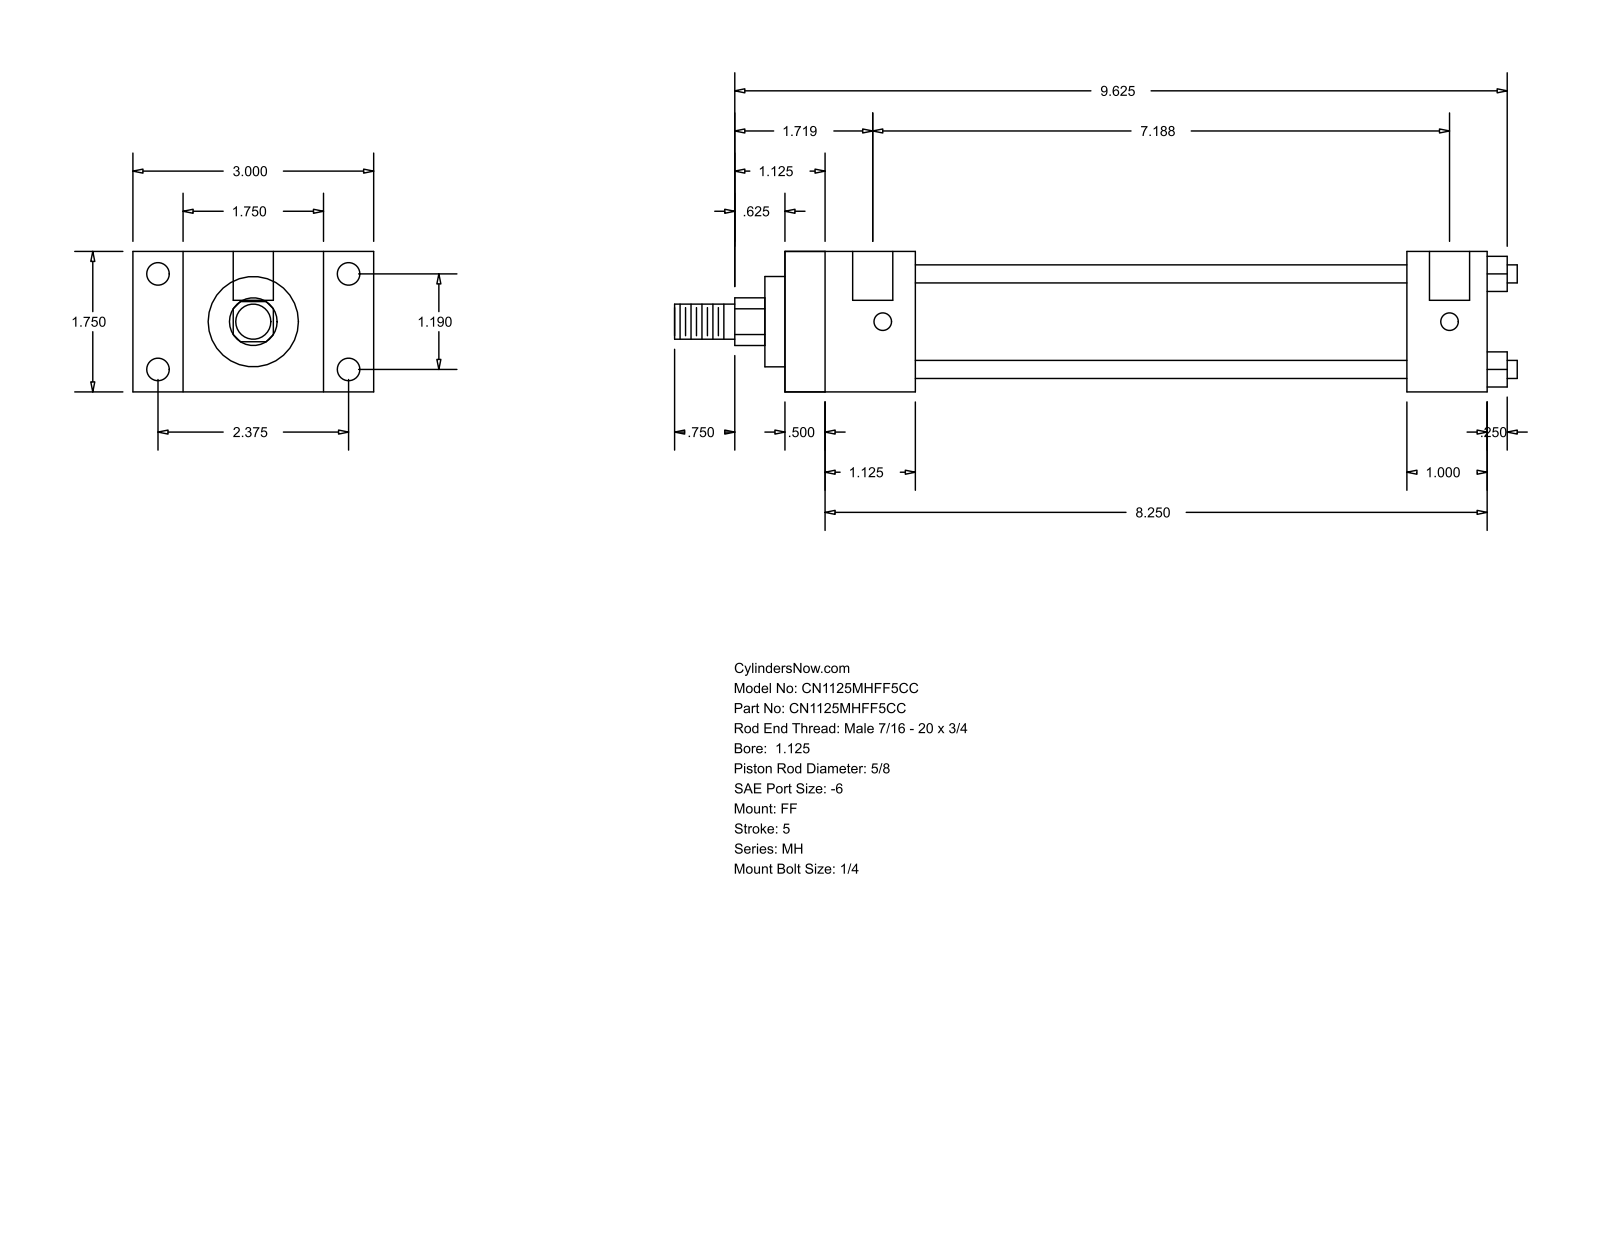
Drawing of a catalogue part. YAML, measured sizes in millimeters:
part_name: "MH_FF__0112_0.625"
step_written_by: "GSSL Pune (CONFIG_CONTROL_DESIGN)"
units: millimeters
bodies: {solids: 0, faces: 92, planar: 64, cylindrical: 28, other: 0}
overall_size: [266.7, 76.2, 44.45]
round_holes:
  - {diameter: 5.56, count: 4}
  - {diameter: 7.14, count: 4}
  - {diameter: 12.7, count: 2}
round_bosses_or_shafts:
  - {diameter: 5.71, count: 4}
  - {diameter: 34.92, count: 1}
  - {diameter: 28.57, count: 1}
  - {diameter: 15.88, count: 1}
  - {diameter: 11.11, count: 1}
partial_cylinders:
  - {radius: 7.54, count: 1}
face_to_face_distances: [44.46, 222.24, 12.69, 209.55, 15.87, 28.58, 60.33, 25.4, 41.27, 196.84]
hole_center_spacings: [30.22, 60.32, 67.47, 179.39, 3.17, 182.56]
